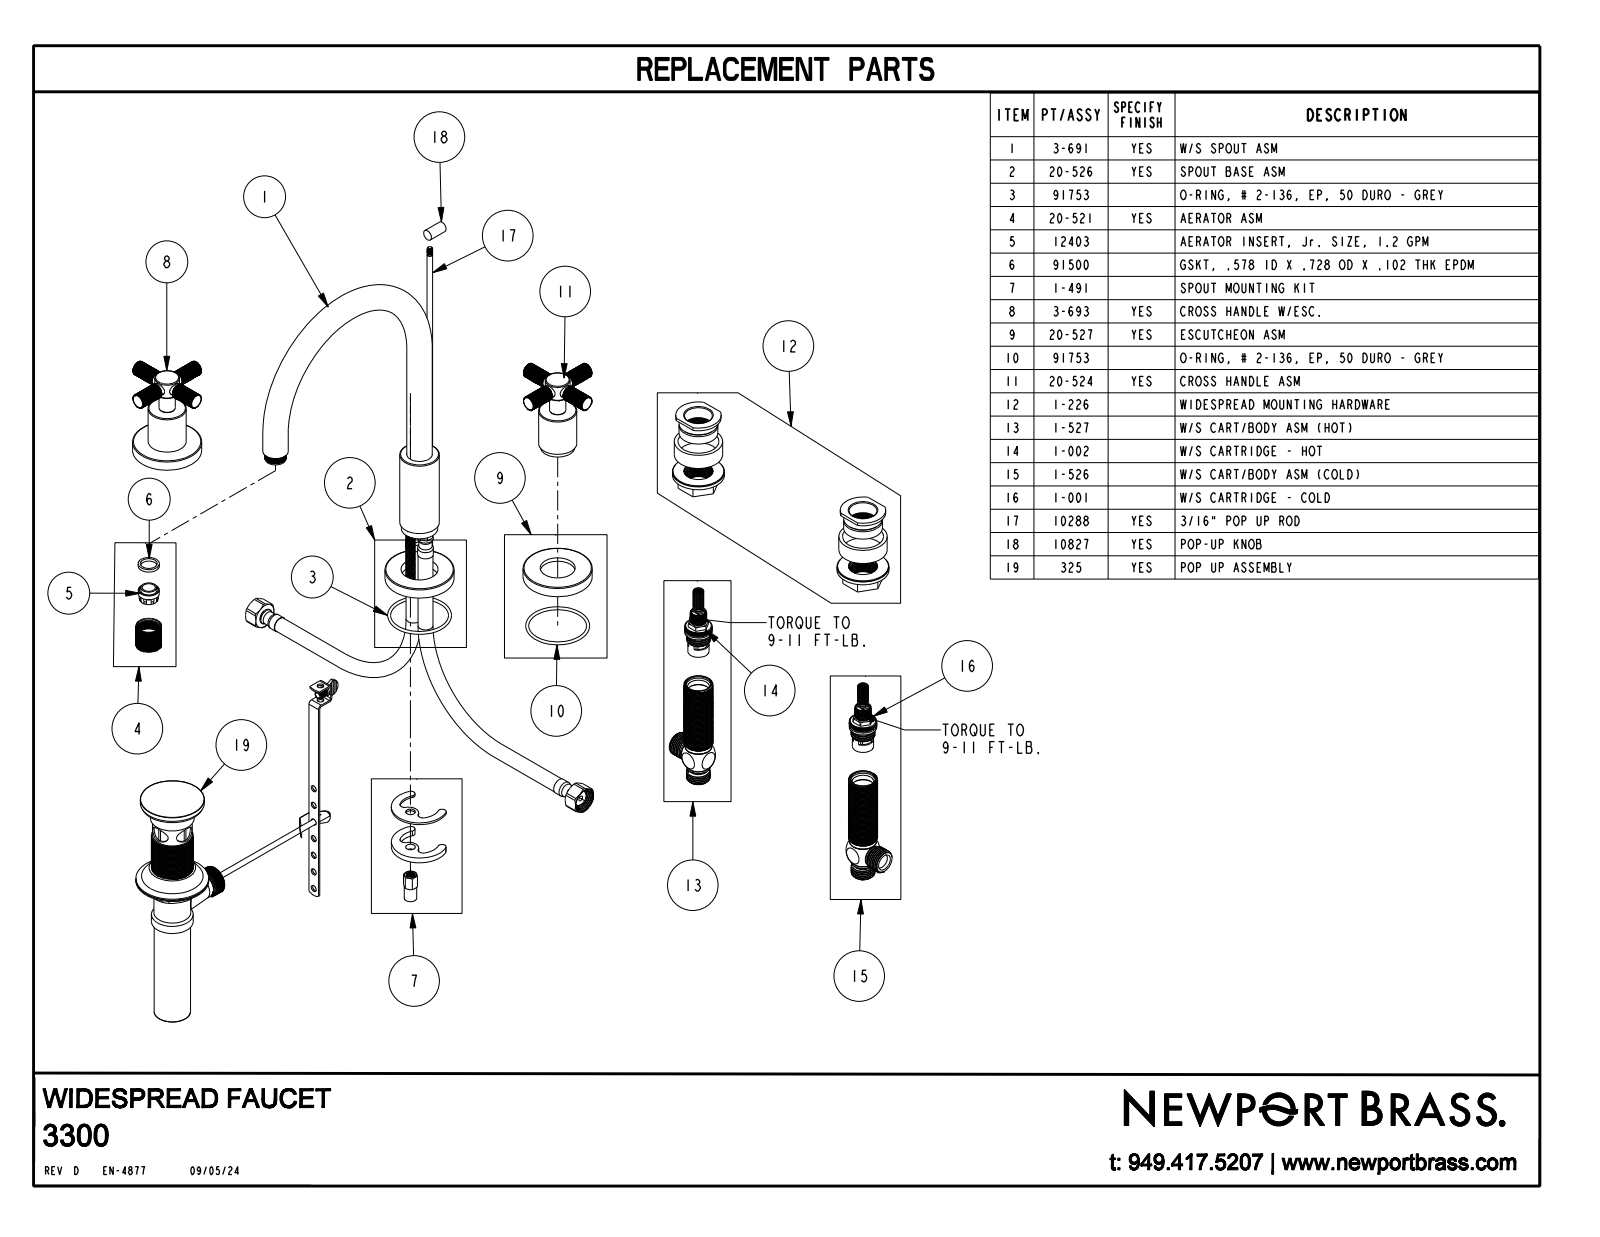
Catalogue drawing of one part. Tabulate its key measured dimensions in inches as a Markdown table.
| quantity | value |
| --- | --- |
| part name | 3300 |
| STEP written by | CREO PARAMETRIC BY PTC INC, 2018400 (CONFIG_CONTROL_DESIGN) |
| units | inches |
| bodies | 3 solids, 26875 faces (168 planar, 5191 cylindrical, 21516 other) |
| overall size | 11.619 × 10.85 × 8.989 |
| volume | 25.55 in³ |
| surface area | 136.9 in² |
| round holes (diameter × count) | 0.465 × 3, 0.56 × 1, 0.62 × 1, 0.691 × 1 |
| round bosses / shafts (diameter × count) | 2.375 × 3, 0.5 × 3, 0.44 × 3, 1.313 × 2, 1.25 × 2, 0.875 × 2, 0.85 × 2, 0.563 × 2 |
| partial cylindrical surfaces (radius × count) | 0.196 × 2, 0.34 × 1 |
| main face-to-face distances | 0.375, 1.775, 1.4, 3.066, 2.691, 1.291, 3.25, 2.875, 1.475, 0.184 |
| hole center spacings | 8 |
